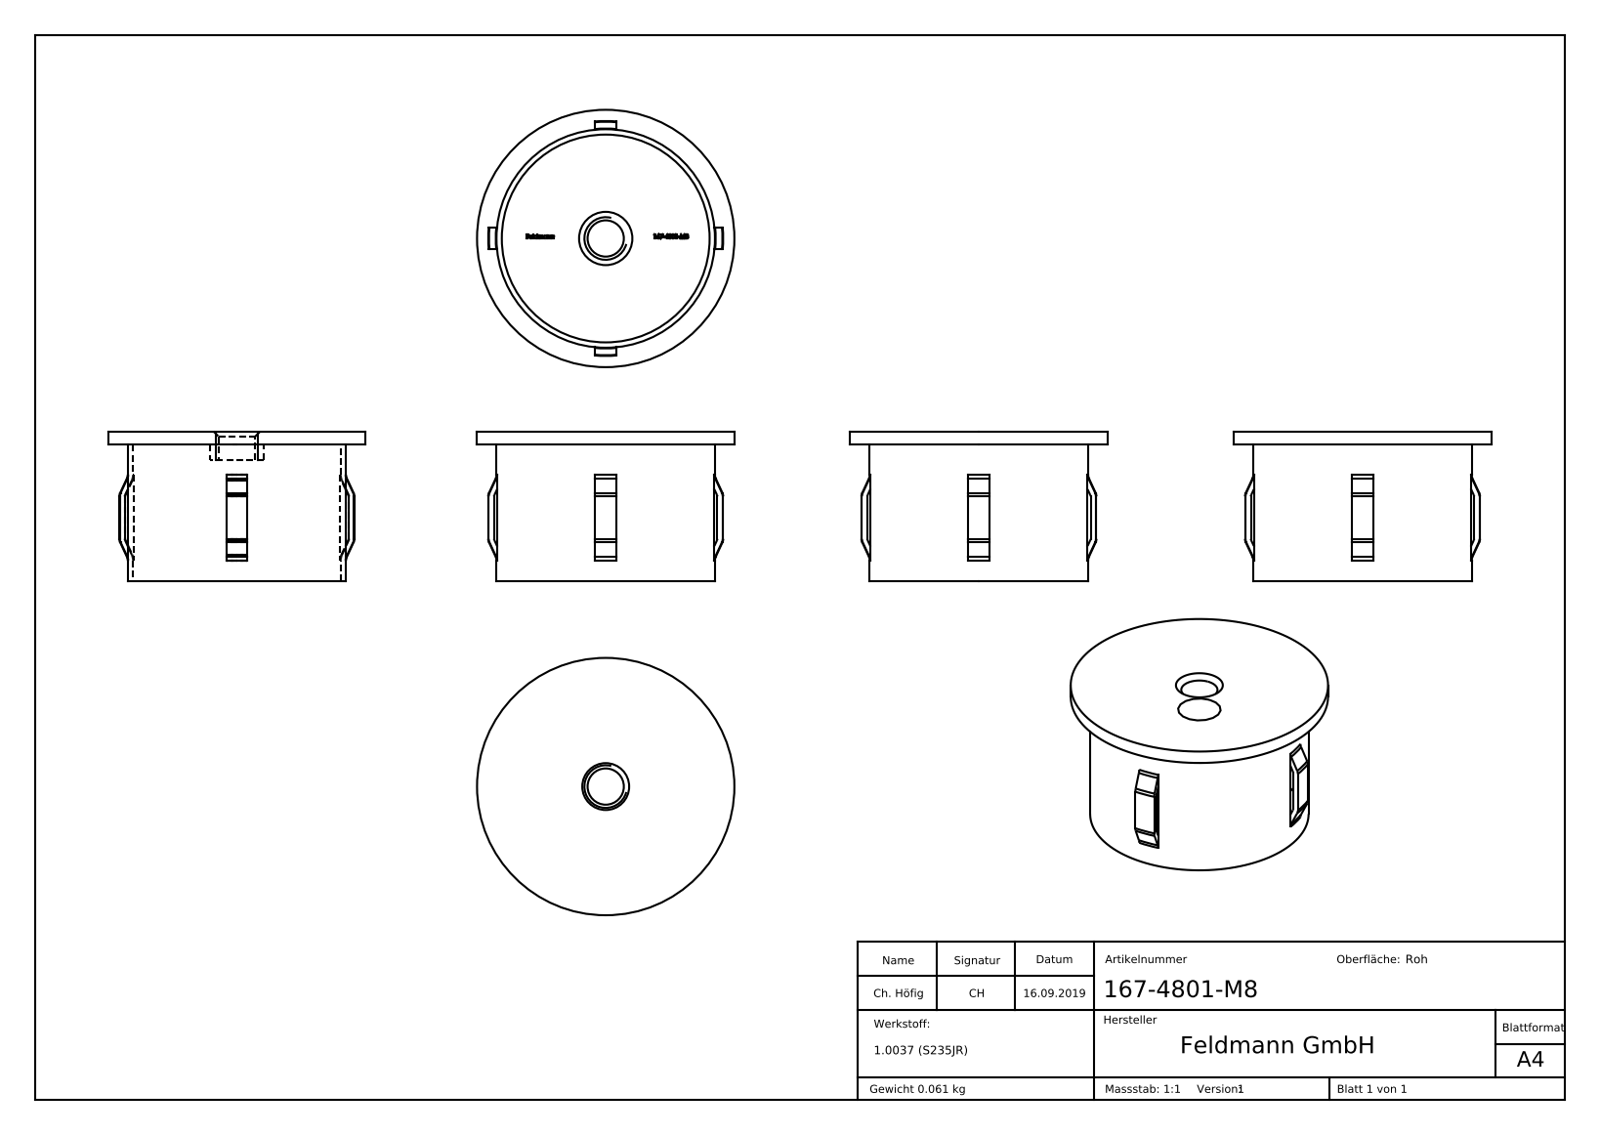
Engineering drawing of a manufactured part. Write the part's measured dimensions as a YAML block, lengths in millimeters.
part_name: "167-4801-M8"
step_written_by: "SolidWorks 2015 (CONFIG_CONTROL_DESIGN)"
units: millimeters
bodies: {solids: 1, faces: 341, planar: 159, cylindrical: 20, other: 162}
overall_size: [48.3, 48.3, 28.2]
volume: 7836
surface_area: 10858
round_holes:
  - {diameter: 6.8, count: 1}
  - {diameter: 39, count: 1}
round_bosses_or_shafts:
  - {diameter: 48.3, count: 1}
  - {diameter: 41, count: 1}
  - {diameter: 10, count: 1}
partial_cylinders:
  - {radius: 21.05, count: 1}
  - {radius: 22.05, count: 1}
face_to_face_distances: [2.5, 25.7, 28.2, 4, 22.9, 2.8, 5.3, 2.4, 25.8, 2.9]
